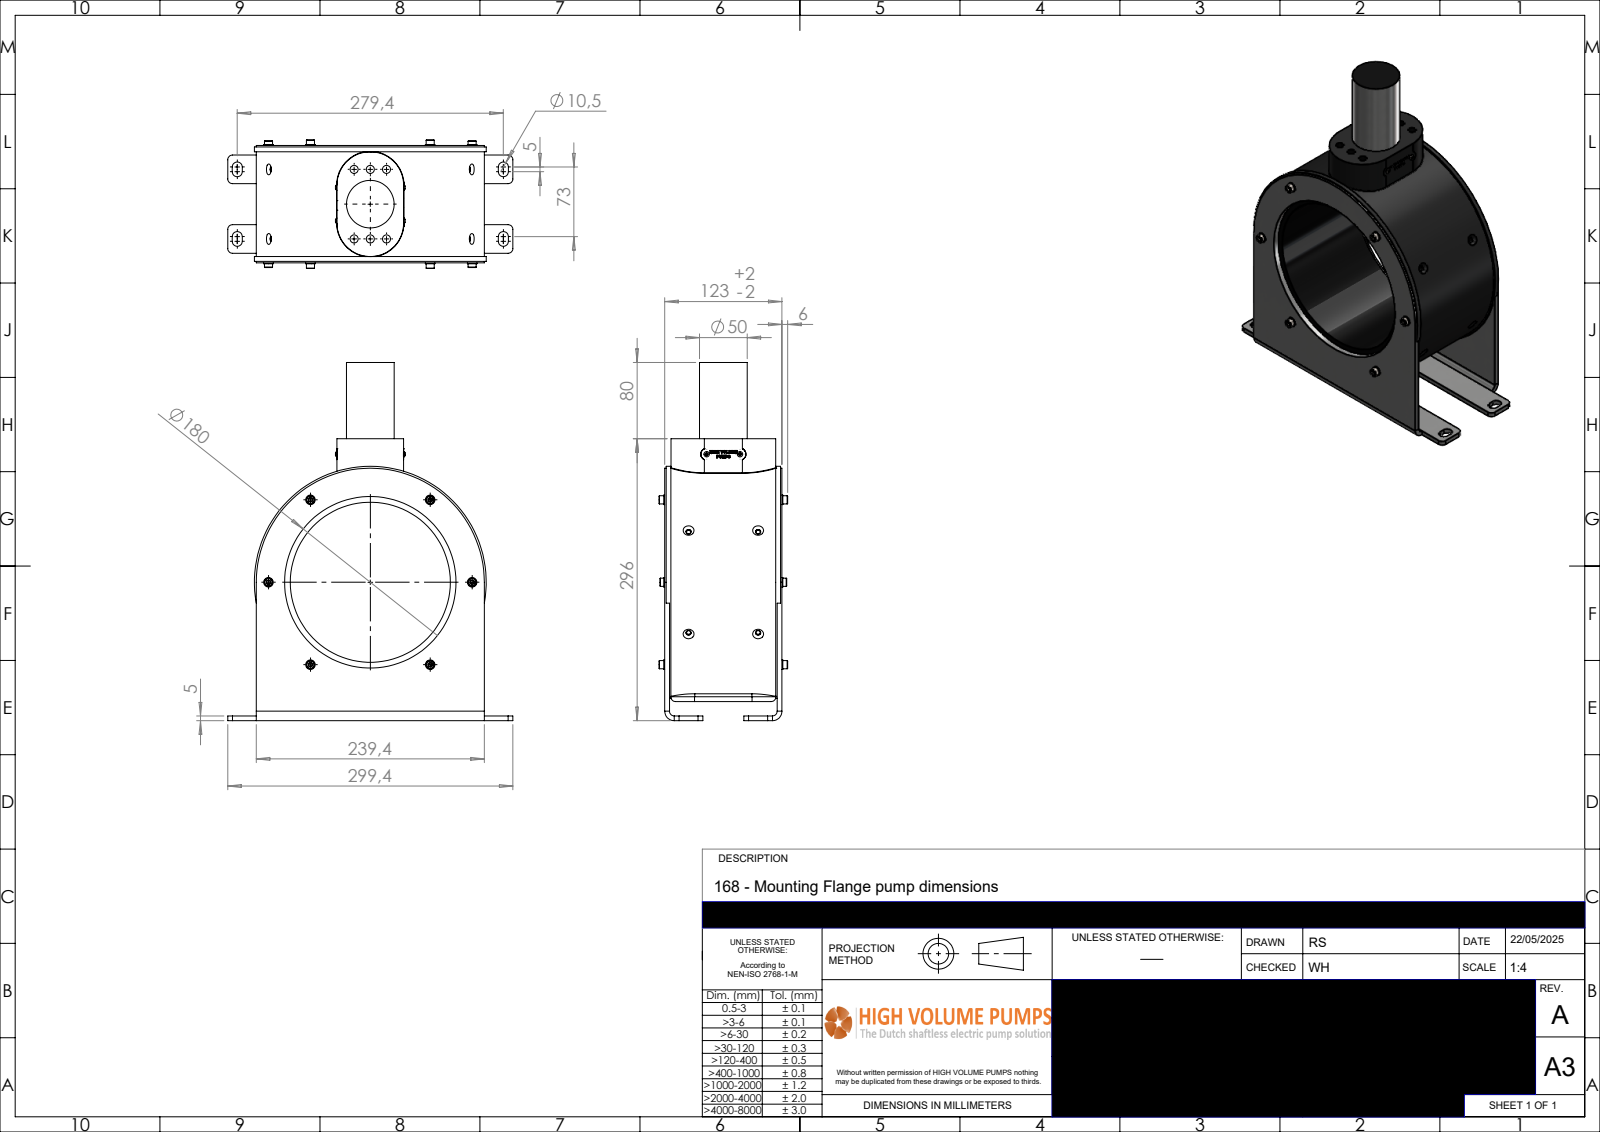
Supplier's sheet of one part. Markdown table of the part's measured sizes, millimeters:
| quantity | value |
| --- | --- |
| part name | P-168-030-rev-A-MF |
| STEP written by | SolidWorks 2024 (AUTOMOTIVE_DESIGN) |
| units | millimeters |
| bodies | 1 solid, 968 faces (573 planar, 203 cylindrical, 192 other) |
| overall size | 375.95 × 299.4 × 135.06 |
| volume | 3 389 000 mm³ |
| surface area | 328 291 mm² |
| round holes (diameter × count) | 4.2 × 6, 5.5 × 6, 8.5 × 6, 3.5 × 2, 168 × 1, 180 × 1 |
| round bosses / shafts (diameter × count) | 10 × 6, 8.5 × 6, 9.64 × 2, 5.7 × 2, 3 × 2, 243.4 × 1, 239.4 × 1, 50 × 1 |
| partial cylindrical surfaces (radius × count) | 5 × 12, 5.25 × 8, 0.5 × 2, 6.15 × 2, 6.25 × 2, 10 × 2, 25 × 2, 34.5 × 2 |
| main face-to-face distances | 5, 123.06, 118.06, 1.5, 116.56, 111.56, 6.5, 113.06, 110.06, 295.94 |
| hole center spacings | 73, 17, 74.95, 34, 80.53, 35 |
